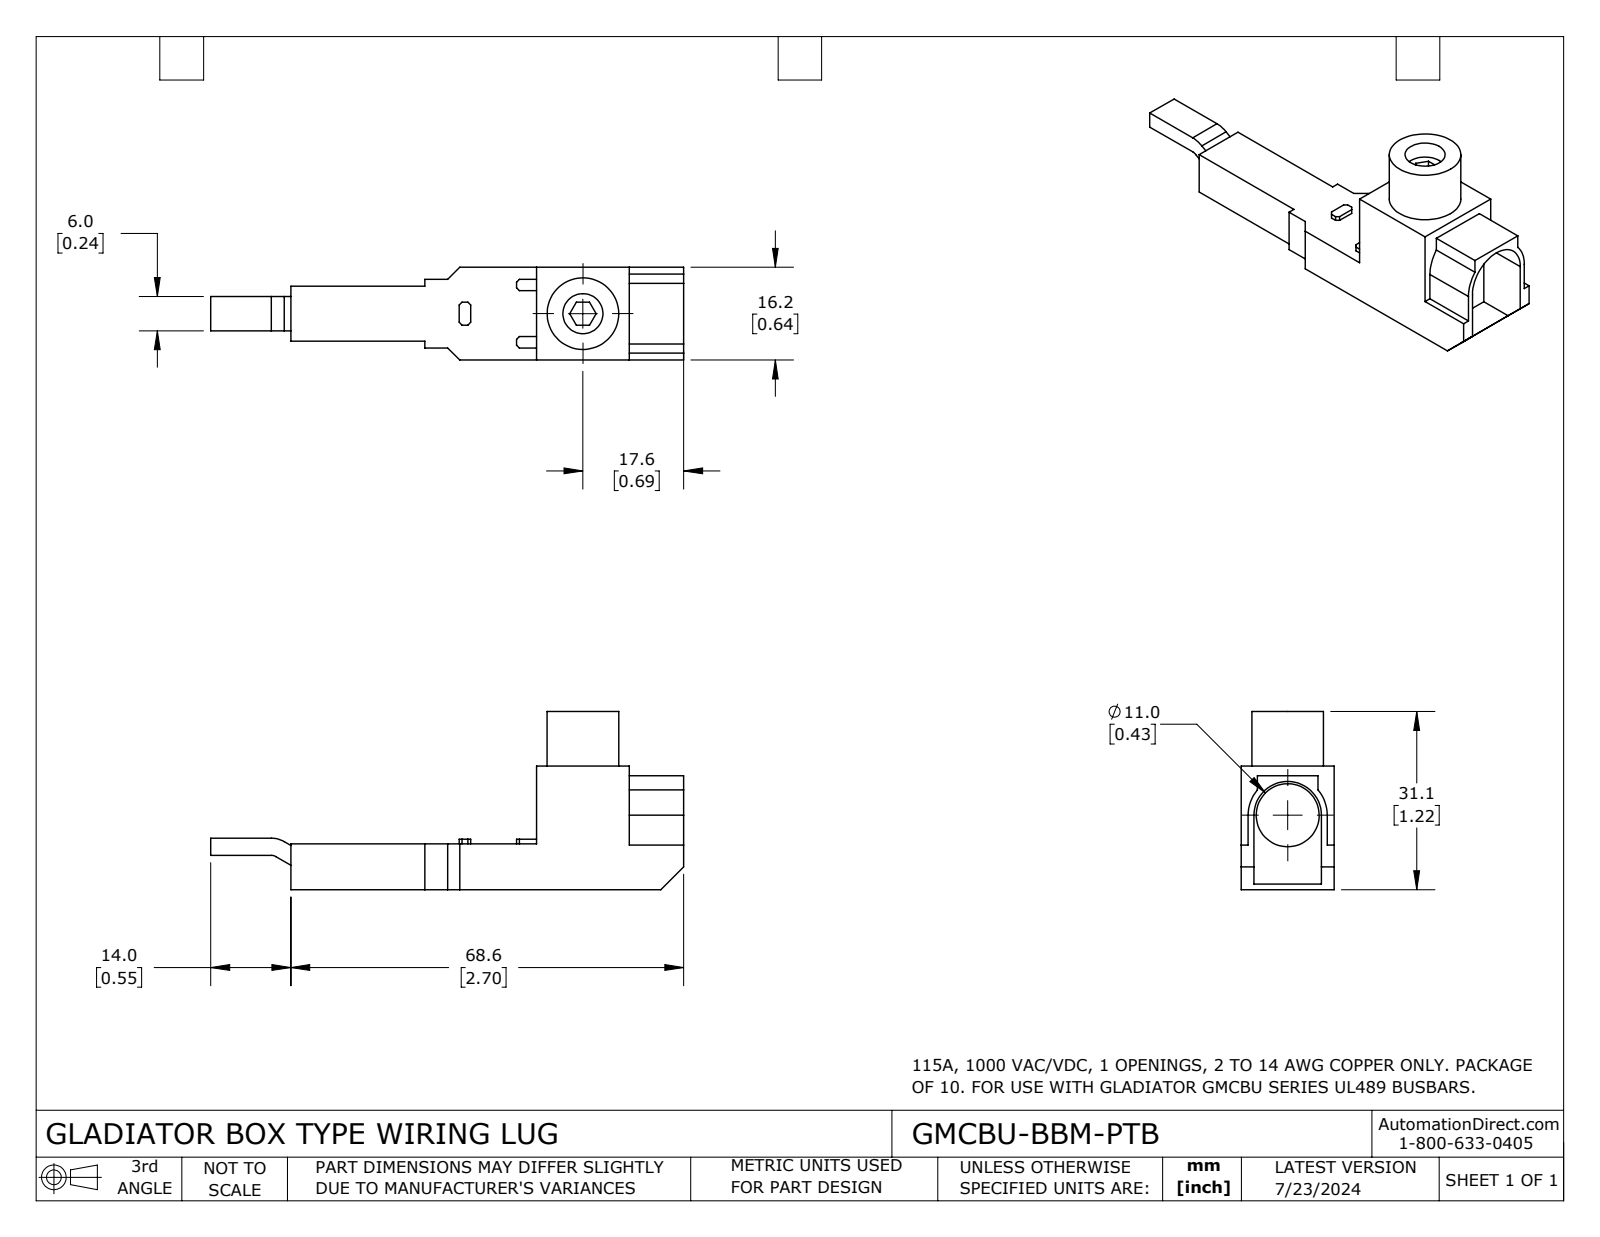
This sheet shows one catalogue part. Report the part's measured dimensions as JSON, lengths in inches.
{"part_name": "GMCBU-BBM-PTB", "step_written_by": "SolidWorks 2023 (CONFIG_CONTROL_DESIGN)", "units": "inches", "bodies": {"solids": 1, "faces": 79, "planar": 67, "cylindrical": 12, "other": 0}, "overall_size": [3.252, 1.224, 0.638], "volume_in3": 0.637, "surface_area_in2": 9.248, "round_holes": [[0.276, 1], [0.433, 1]], "round_bosses_or_shafts": [[0.492, 1]], "partial_cylinders_radius": [[0.059, 1], [0.177, 1], [0.232, 1], [0.272, 1]], "face_to_face_distances": [0.638, 0.315, 0.508, 0.13, 0.039, 0.551, 0.087, 0.043, 0.421, 0.047]}
